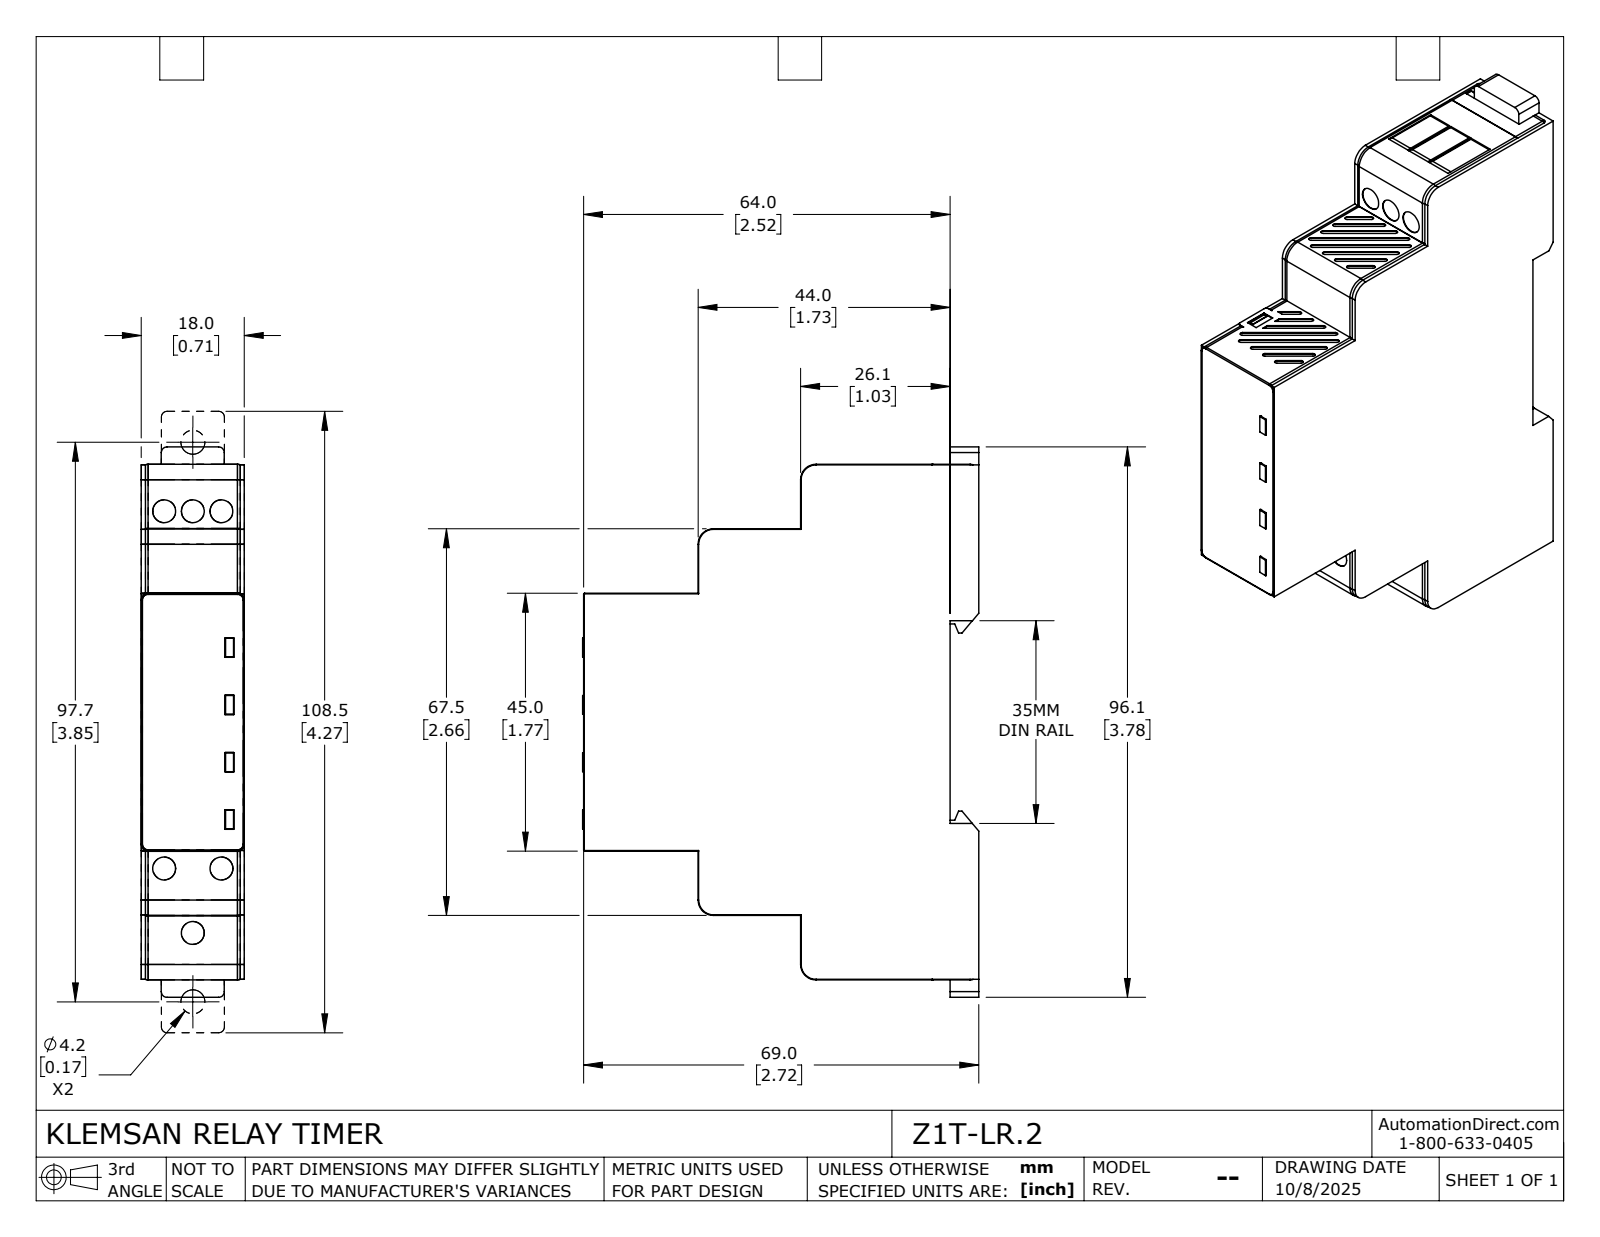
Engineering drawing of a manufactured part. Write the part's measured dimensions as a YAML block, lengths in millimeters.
part_name: "Z1T-LR.2"
step_written_by: "SolidWorks 2024 (CONFIG_CONTROL_DESIGN)"
units: millimeters
bodies: {solids: 3, faces: 440, planar: 280, cylindrical: 60, other: 100}
overall_size: [96.07, 69.15, 18]
volume: 83847
surface_area: 17884
round_holes:
  - {diameter: 4.2, count: 2}
  - {diameter: 4, count: 1}
partial_cylinders:
  - {radius: 1.2, count: 16}
  - {radius: 0.2, count: 4}
  - {radius: 1, count: 4}
  - {radius: 2.6, count: 4}
  - {radius: 2.7, count: 4}
  - {radius: 0.5, count: 2}
  - {radius: 1.5, count: 2}
face_to_face_distances: [18, 3.5, 14.5, 11.25, 64, 5, 69, 22.5, 67.4, 67.5]
hole_center_spacings: [5.83, 79.43, 85.26]
